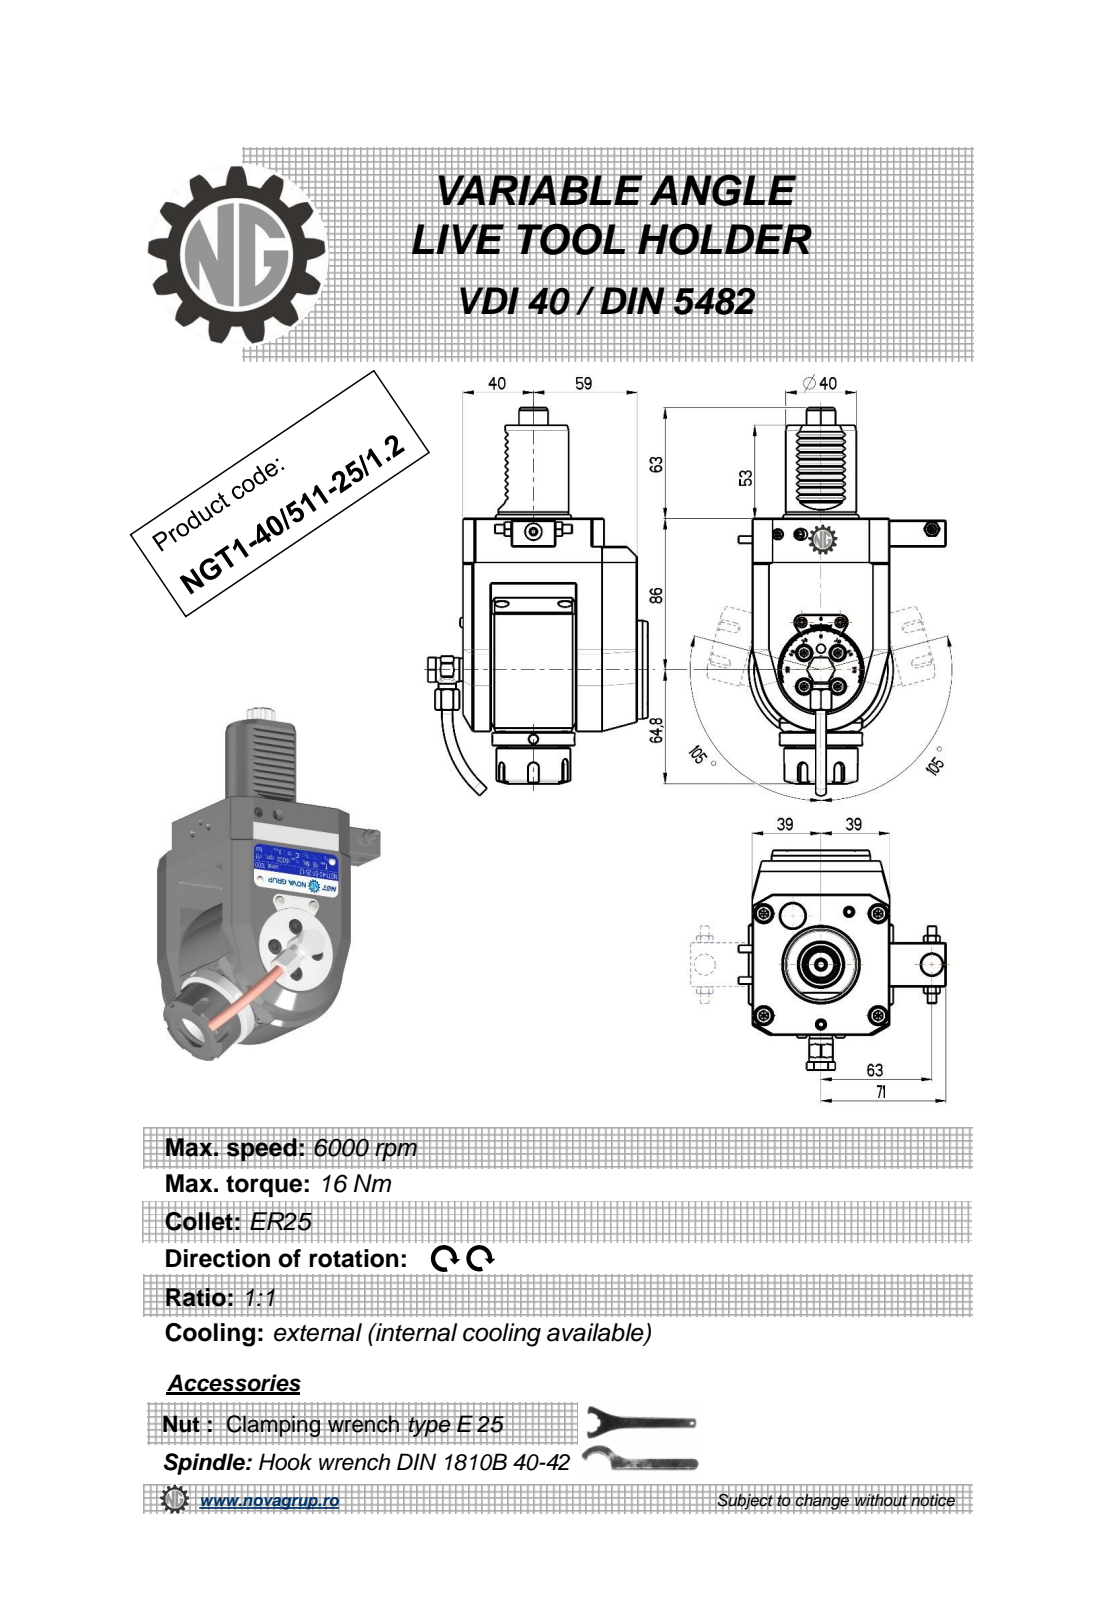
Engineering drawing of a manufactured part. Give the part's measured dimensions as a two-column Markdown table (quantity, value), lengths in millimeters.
| quantity | value |
| --- | --- |
| part name | NGT1_40_511_25_1_2 |
| STEP written by | PRO/ENGINEER BY PARAMETRIC TECHNOLOGY CORPORATION, 2010280 (CONFIG_CONTROL_DESIGN) |
| units | millimeters |
| bodies | 1 solid, 607 faces (226 planar, 171 cylindrical, 210 other) |
| overall size | 220.67 × 124.9 × 112 |
| volume | 908 691 mm³ |
| surface area | 83 488 mm² |
| round holes (diameter × count) | 4 × 3, 4.2 × 2, 5 × 2, 3 × 1, 4.5 × 1, 5.3 × 1, 6.2 × 1, 9 × 1, 9.5 × 1, 11 × 1, 12 × 1, 20.3 × 1 |
| round bosses / shafts (diameter × count) | 10 × 2, 6 × 2, 5.7 × 2, 82 × 1, 56 × 1, 47 × 1, 42 × 1, 40 × 1 |
| partial cylindrical surfaces (radius × count) | 3.03 × 18, 0.26 × 12, 0.3 × 10, 3 × 5, 0.5 × 4, 1 × 2, 10 × 2, 6.75 × 1 |
| main face-to-face distances | 16, 37, 99, 78, 64, 6, 105, 21, 89, 83 |
| hole center spacings | 0.4, 39.45, 49, 49.4, 63, 79.81, 80.06, 101.83 |
